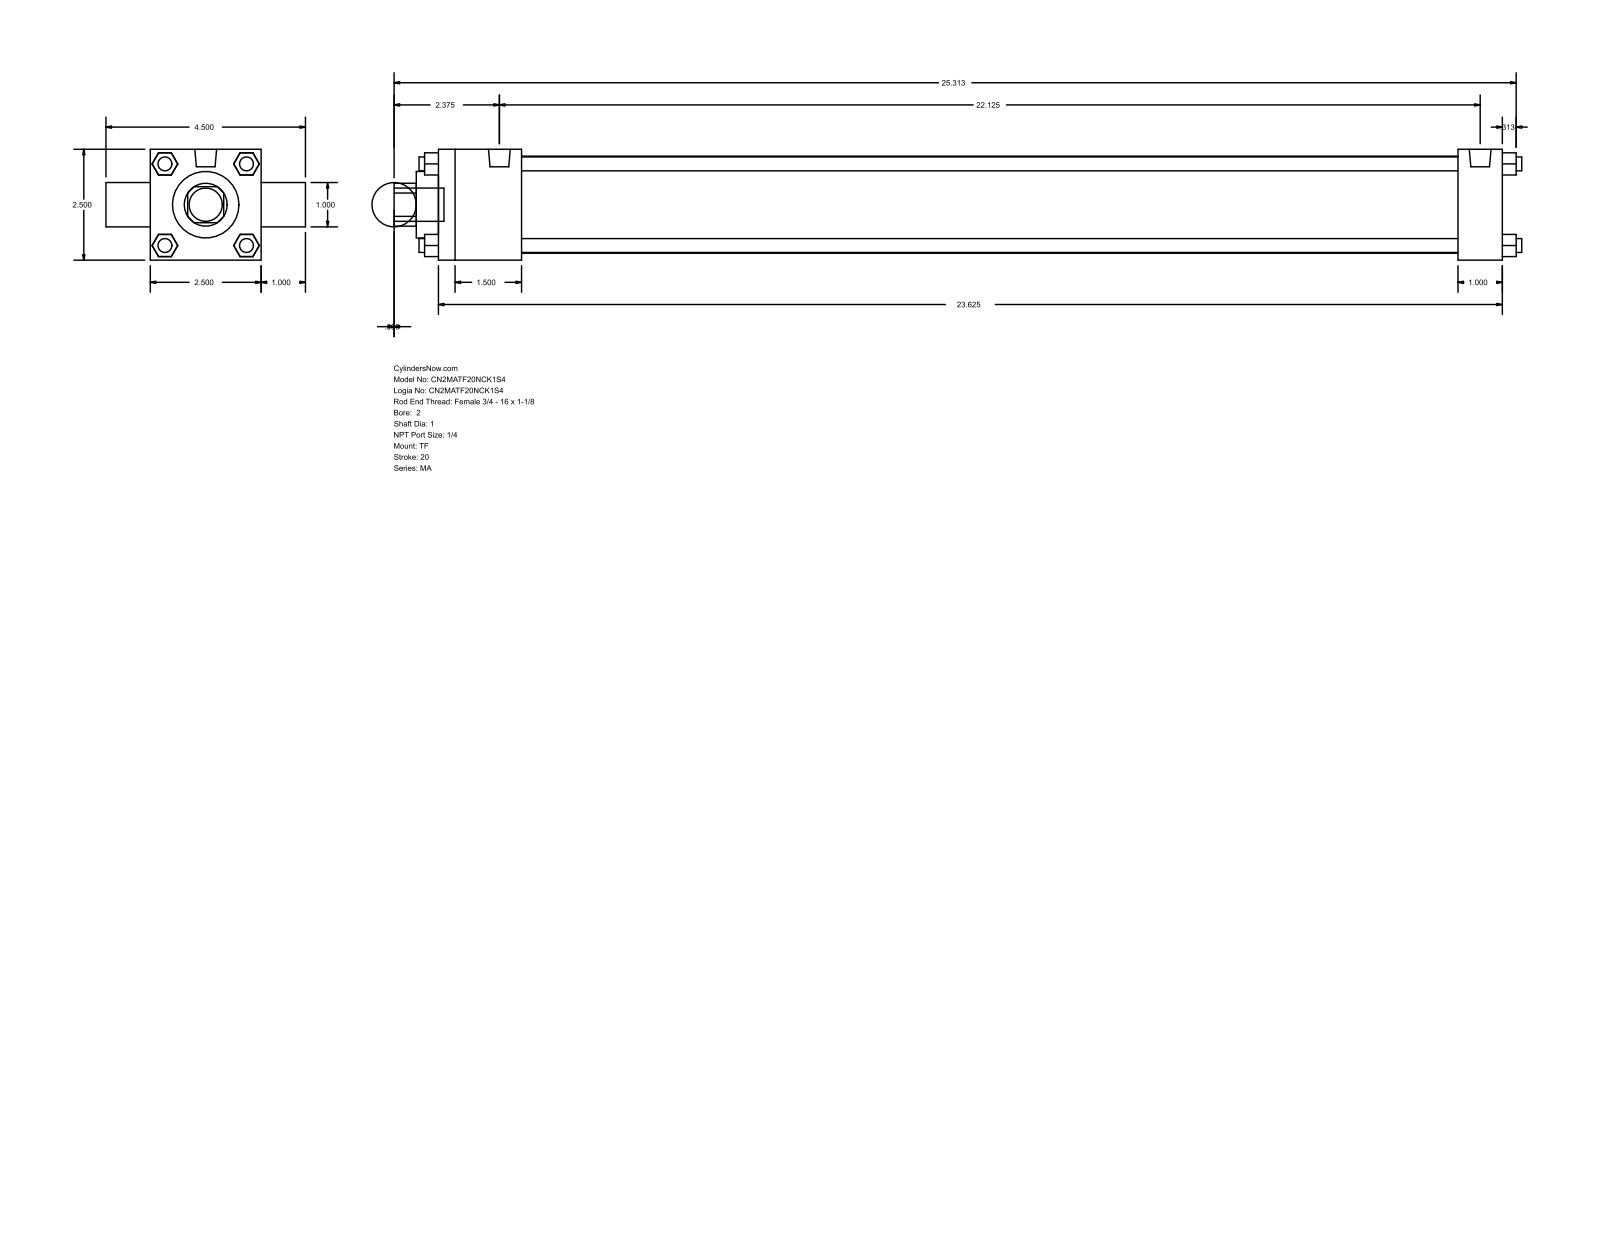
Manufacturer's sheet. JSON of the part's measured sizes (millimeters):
{"part_name": "MA_TF__0200_1", "step_written_by": "GSSL Pune (CONFIG_CONTROL_DESIGN)", "units": "millimeters", "bodies": {"solids": 0, "faces": 120, "planar": 92, "cylindrical": 28, "other": 0}, "overall_size": [646.11, 114.3, 63.5], "round_holes": [[25.4, 2], [38.1, 1], [55.63, 1]], "round_bosses_or_shafts": [[7.94, 7], [12.49, 2], [19.05, 1]], "partial_cylinders_radius": [[12.29, 1]], "face_to_face_distances": [63.5, 25.4, 609.6, 12.7, 47.63, 584.2, 536.57, 561.97, 88.9, 23.37]}
